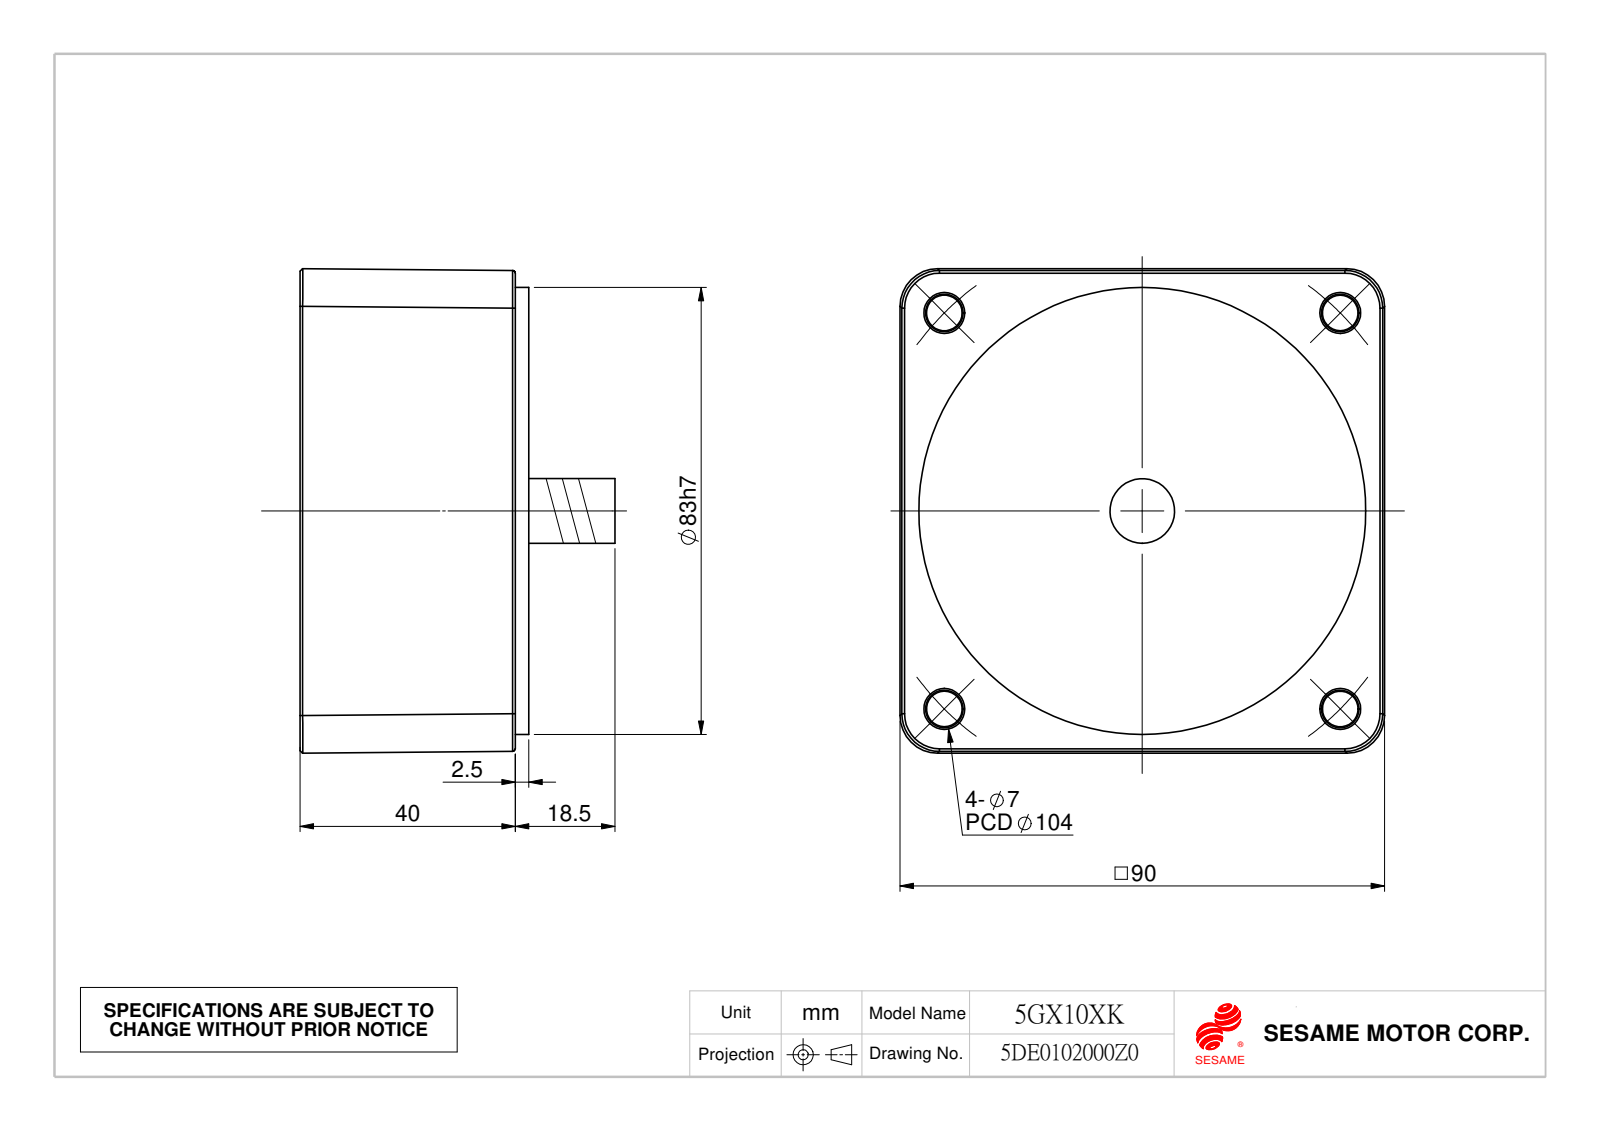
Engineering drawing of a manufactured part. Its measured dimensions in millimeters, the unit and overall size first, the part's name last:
Units: millimetres
Overall size (bounding box): 89.99 × 89.99 × 58.5
Round holes (diameter × count): ⌀3.3 ×4, ⌀4.2 ×4, ⌀7.6 ×4, ⌀4 ×2, ⌀10 ×1, ⌀82.97 ×1, ⌀85.77 ×1
Round bosses / shafts (diameter × count): ⌀4 ×5, ⌀8 ×4, ⌀14 ×2, ⌀83 ×1, ⌀82.8 ×1, ⌀64 ×1, ⌀19 ×1, ⌀16 ×1
Partial cylindrical surfaces — rounded edges, fillets, slot ends (radius × count): R0.5 ×4, R7 ×4
Main face-to-face distances: 33.6, 2.5, 5.4, 39, 2.2, 3.2, 36.8, 36.5, 34.3, 31.1
Hole centre spacings: 36, 52, 73.54, 16.11, 51.27, 55.48, 57.12, 61.94
Volume: 303 893 mm³ · Surface area: 50 822 mm²
Bodies: 8 solids, 319 faces (105 planar, 86 cylindrical, 128 other)
Part name (STEP PRODUCT): 5GX10X齒箱外型_G583-M(GX); 定位銷 4 x 6L_Parallel Pin ISO 8734 - 4 x 10 - A - St
STEP written by: SolidWorks 2010 (CONFIG_CONTROL_DESIGN)
